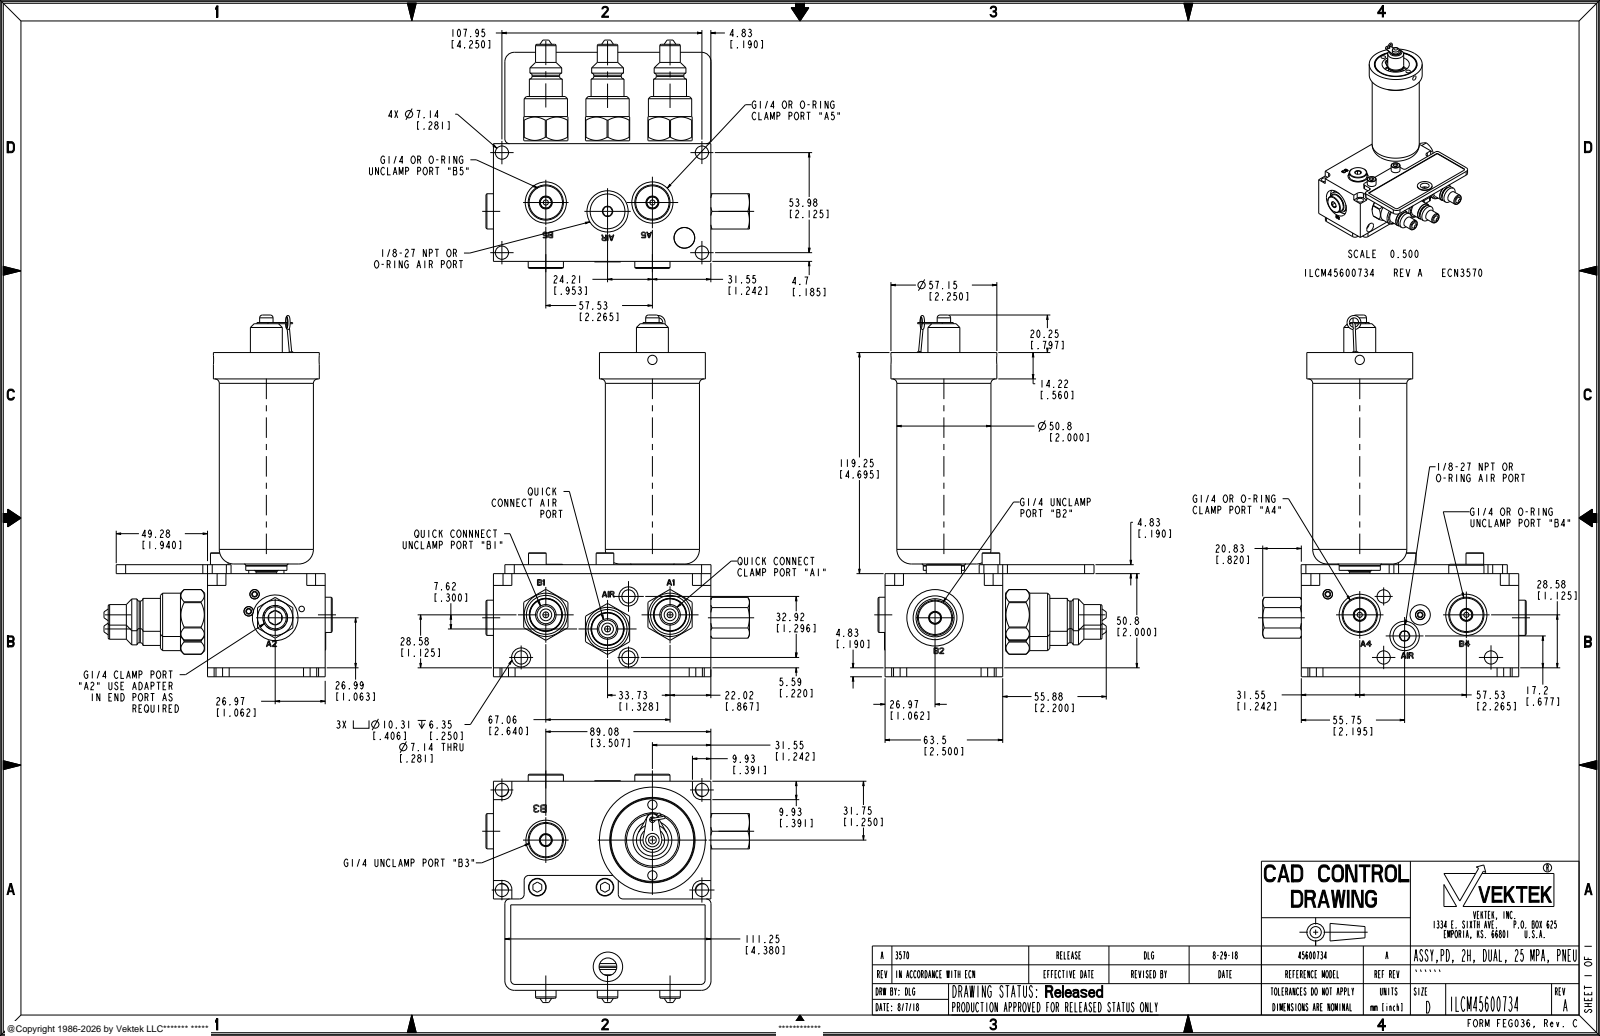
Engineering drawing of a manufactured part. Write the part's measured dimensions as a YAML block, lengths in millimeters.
part_name: "ILCM45600734; 45600511; 30871966"
step_written_by: "PRO/ENGINEER BY PARAMETRIC TECHNOLOGY CORPORATION, 2013320 (CONFIG_CONTROL_DESIGN)"
units: millimeters
bodies: {solids: 8, faces: 1854, planar: 1094, cylindrical: 370, other: 390}
overall_size: [195.1, 142.2, 123.2]
volume: 588300
surface_area: 137500
round_holes:
  - {diameter: 7.1, count: 8}
  - {diameter: 22.2, count: 5}
  - {diameter: 3.1, count: 4}
  - {diameter: 5.1, count: 4}
  - {diameter: 5, count: 3}
  - {diameter: 10.3, count: 3}
  - {diameter: 13.1, count: 3}
  - {diameter: 2, count: 2}
  - {diameter: 3, count: 2}
  - {diameter: 11.9, count: 2}
  - {diameter: 21.5, count: 2}
  - {diameter: 31.8, count: 2}
round_bosses_or_shafts:
  - {diameter: 19, count: 5}
  - {diameter: 5, count: 4}
  - {diameter: 4.5, count: 4}
  - {diameter: 23.4, count: 3}
  - {diameter: 17.8, count: 3}
  - {diameter: 17.1, count: 3}
  - {diameter: 14.9, count: 3}
  - {diameter: 11.1, count: 3}
partial_cylinders:
  - {radius: 2.3, count: 70}
  - {radius: 3.6, count: 12}
  - {radius: 2.5, count: 6}
  - {radius: 4.7, count: 4}
  - {radius: 5.1, count: 3}
  - {radius: 13.6, count: 3}
  - {radius: 20.6, count: 2}
  - {radius: 2.7, count: 1}
face_to_face_distances: [50.8, 4.8, 55.6, 63.5, 4.3, 55.1, 59.9, 117.3, 0.5, 60.5]
hole_center_spacings: [19.1, 19.1, 24.7, 54, 57.5, 59, 60.6, 108]
